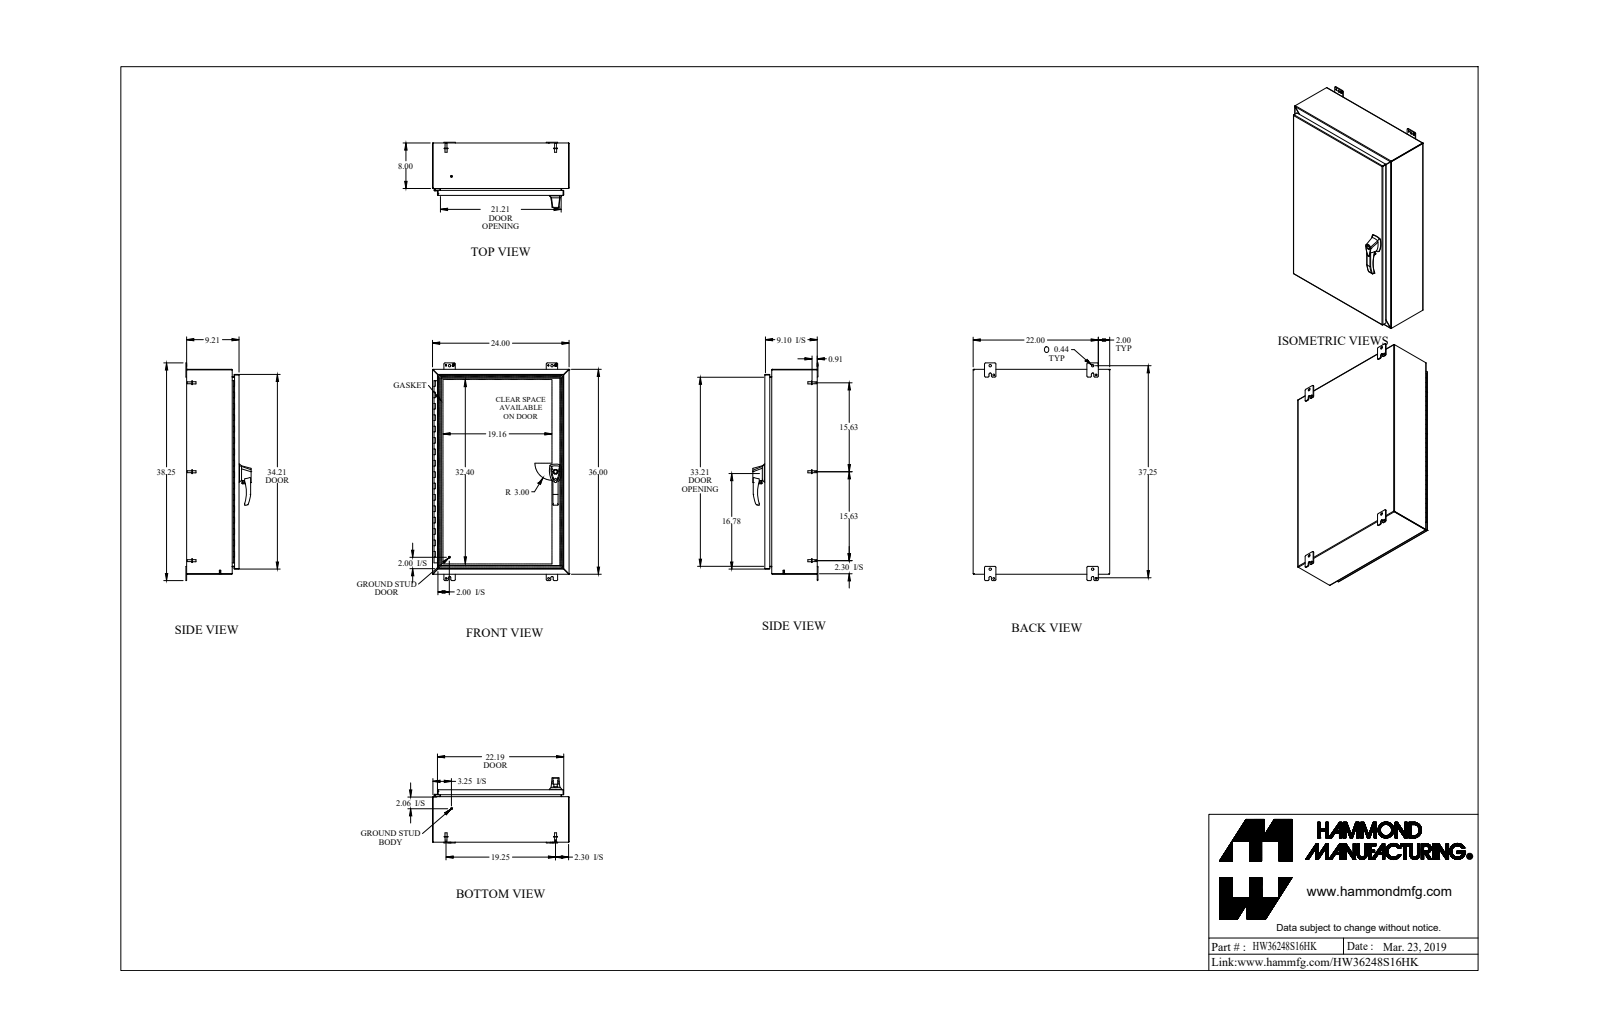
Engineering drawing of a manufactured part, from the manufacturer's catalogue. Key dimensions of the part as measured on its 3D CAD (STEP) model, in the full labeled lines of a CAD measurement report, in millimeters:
Part name (STEP PRODUCT): HW36248S16HK
STEP written by: SolidWorks 2018 (AUTOMOTIVE_DESIGN)
Units: millimetres
Bodies: 44 solids, 1542 faces (720 planar, 658 cylindrical, 164 other)
Overall size (bounding box): 971.6 × 609.6 × 290.8
Volume: 4 131 000 mm³ · Surface area: 4 243 000 mm²
Round holes (diameter × count): ⌀4.5 ×6, ⌀8 ×5, ⌀6.4 ×3, ⌀6.7 ×3, ⌀10.5 ×3, ⌀5 ×2, ⌀6.5 ×2, ⌀10 ×2, ⌀11.1 ×2, ⌀2.8 ×1, ⌀5.9 ×1, ⌀8.4 ×1
Round bosses / shafts (diameter × count): ⌀9.5 ×11, ⌀6.4 ×7, ⌀16.5 ×6, ⌀8.4 ×6, ⌀4 ×6, ⌀25.4 ×3, ⌀13 ×3, ⌀16 ×2
Partial cylindrical surfaces — rounded edges, fillets, slot ends (radius × count): R6.4 ×27, R4.8 ×24, R0.9 ×20, R2.7 ×20, R1.5 ×12, R3.2 ×9, R1.1 ×8, R5.5 ×8
Main face-to-face distances: 1.8, 232.1, 230.3, 1.8, 232.1, 233.9, 607.8, 912.6, 201.4, 605.9
Hole centre spacings: 28.2, 358.6, 358.6, 717.2, 358.6, 457.2, 949.5, 25.5
